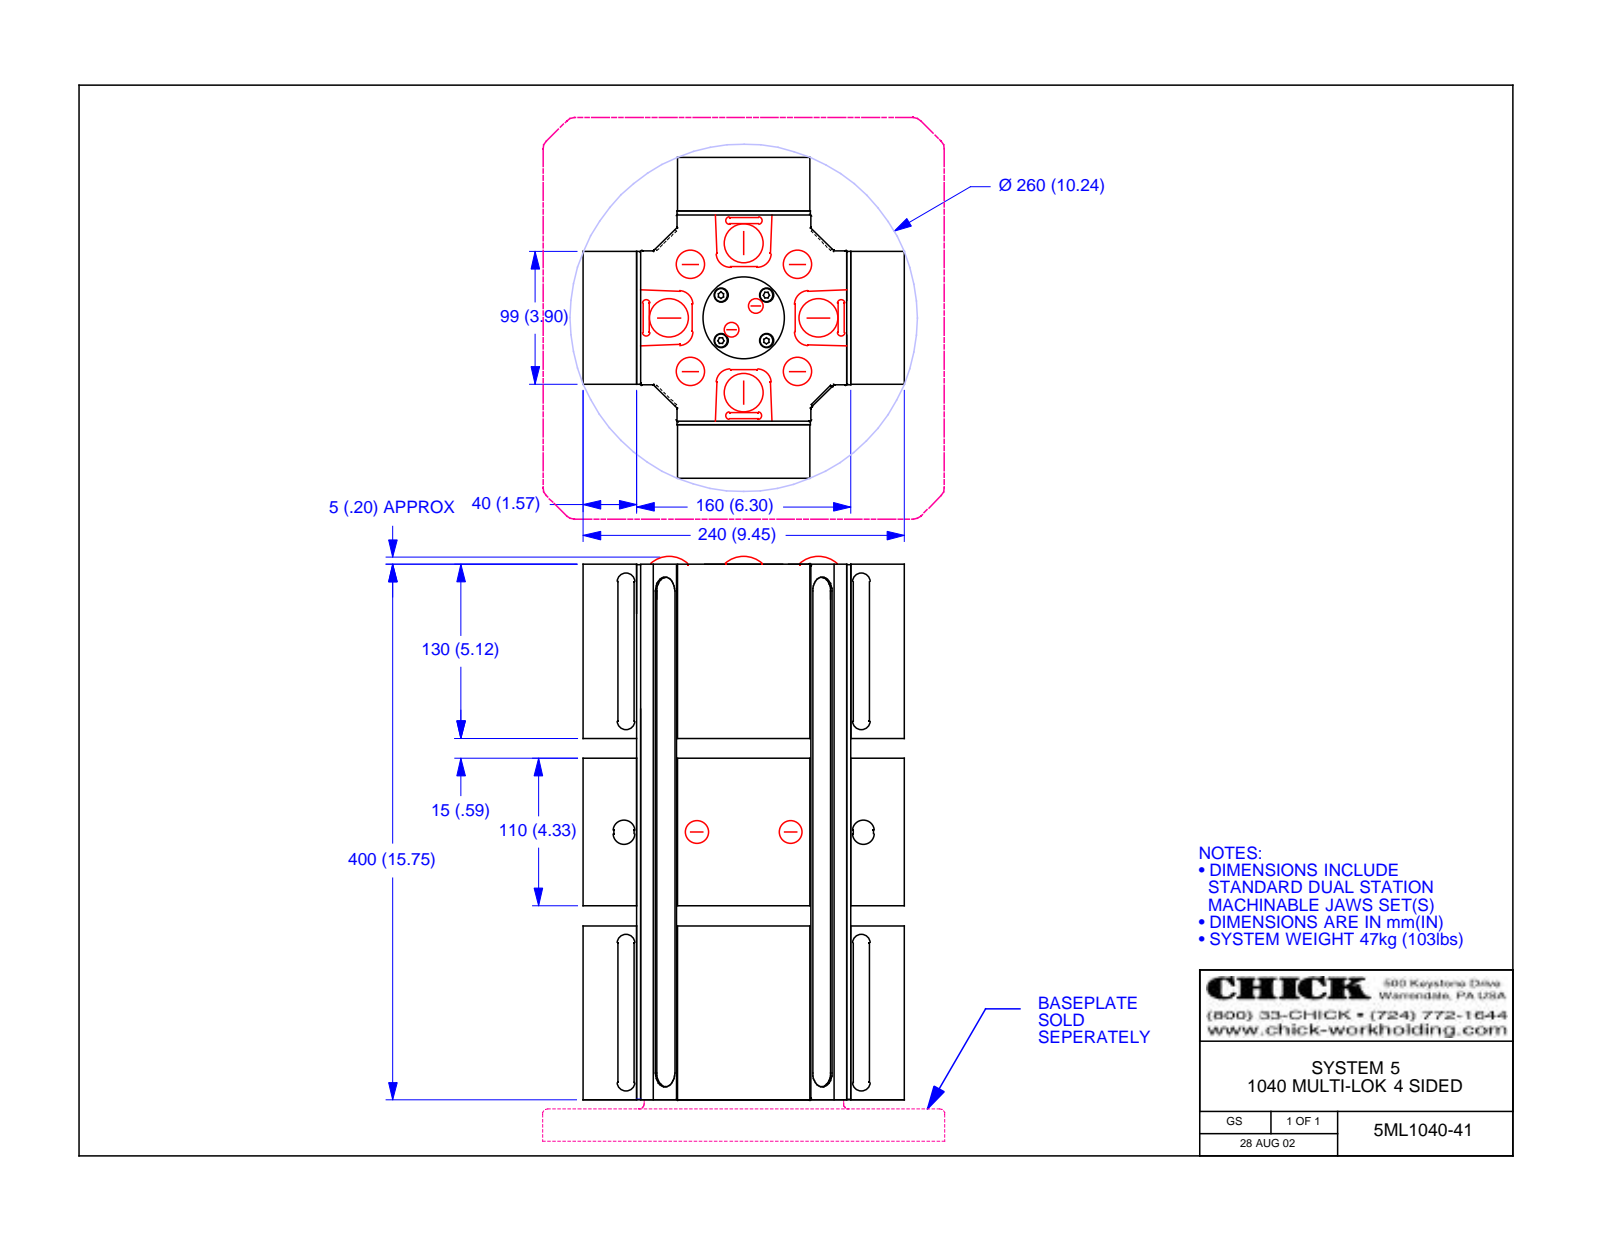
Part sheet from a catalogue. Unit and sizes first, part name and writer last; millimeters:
Units: millimetres
Overall size (bounding box): 405.5 × 239.4 × 239.4
Round holes (diameter × count): ⌀6.65 ×12, ⌀9 ×12, ⌀14.15 ×12, ⌀19.34 ×12, ⌀8.65 ×8, ⌀10.11 ×8, ⌀12.7 ×8, ⌀10 ×6, ⌀4.06 ×4, ⌀4.92 ×4, ⌀6.87 ×4, ⌀8.4 ×4
Round bosses / shafts (diameter × count): ⌀8.4 ×8, ⌀7.67 ×4, ⌀4.76 ×4
Partial cylindrical surfaces — rounded edges, fillets, slot ends (radius × count): R1.5 ×88, R0.4 ×16, R1.2 ×16, R4.8 ×16, R11.1 ×16, R1.65 ×8, R2.83 ×8, R3 ×8
Main face-to-face distances: 3, 157, 39.7, 42.7, 196.7, 199.7, 154, 160, 107.69, 131.71
Hole centre spacings: 70, 1.22, 25.5, 35, 45.65, 58.6, 67.19, 70.46
Volume: 12 920 000 mm³ · Surface area: 1 269 000 mm²
Bodies: 17 solids, 2503 faces (1306 planar, 484 cylindrical, 713 other)
Part name (STEP PRODUCT): 5ML1040-41; 5CLM1040-41; 5CP1040-ST; 5DS1040-10-40 (+2 more)
STEP written by: Autodesk Inventor 2013 (AUTOMOTIVE_DESIGN)
